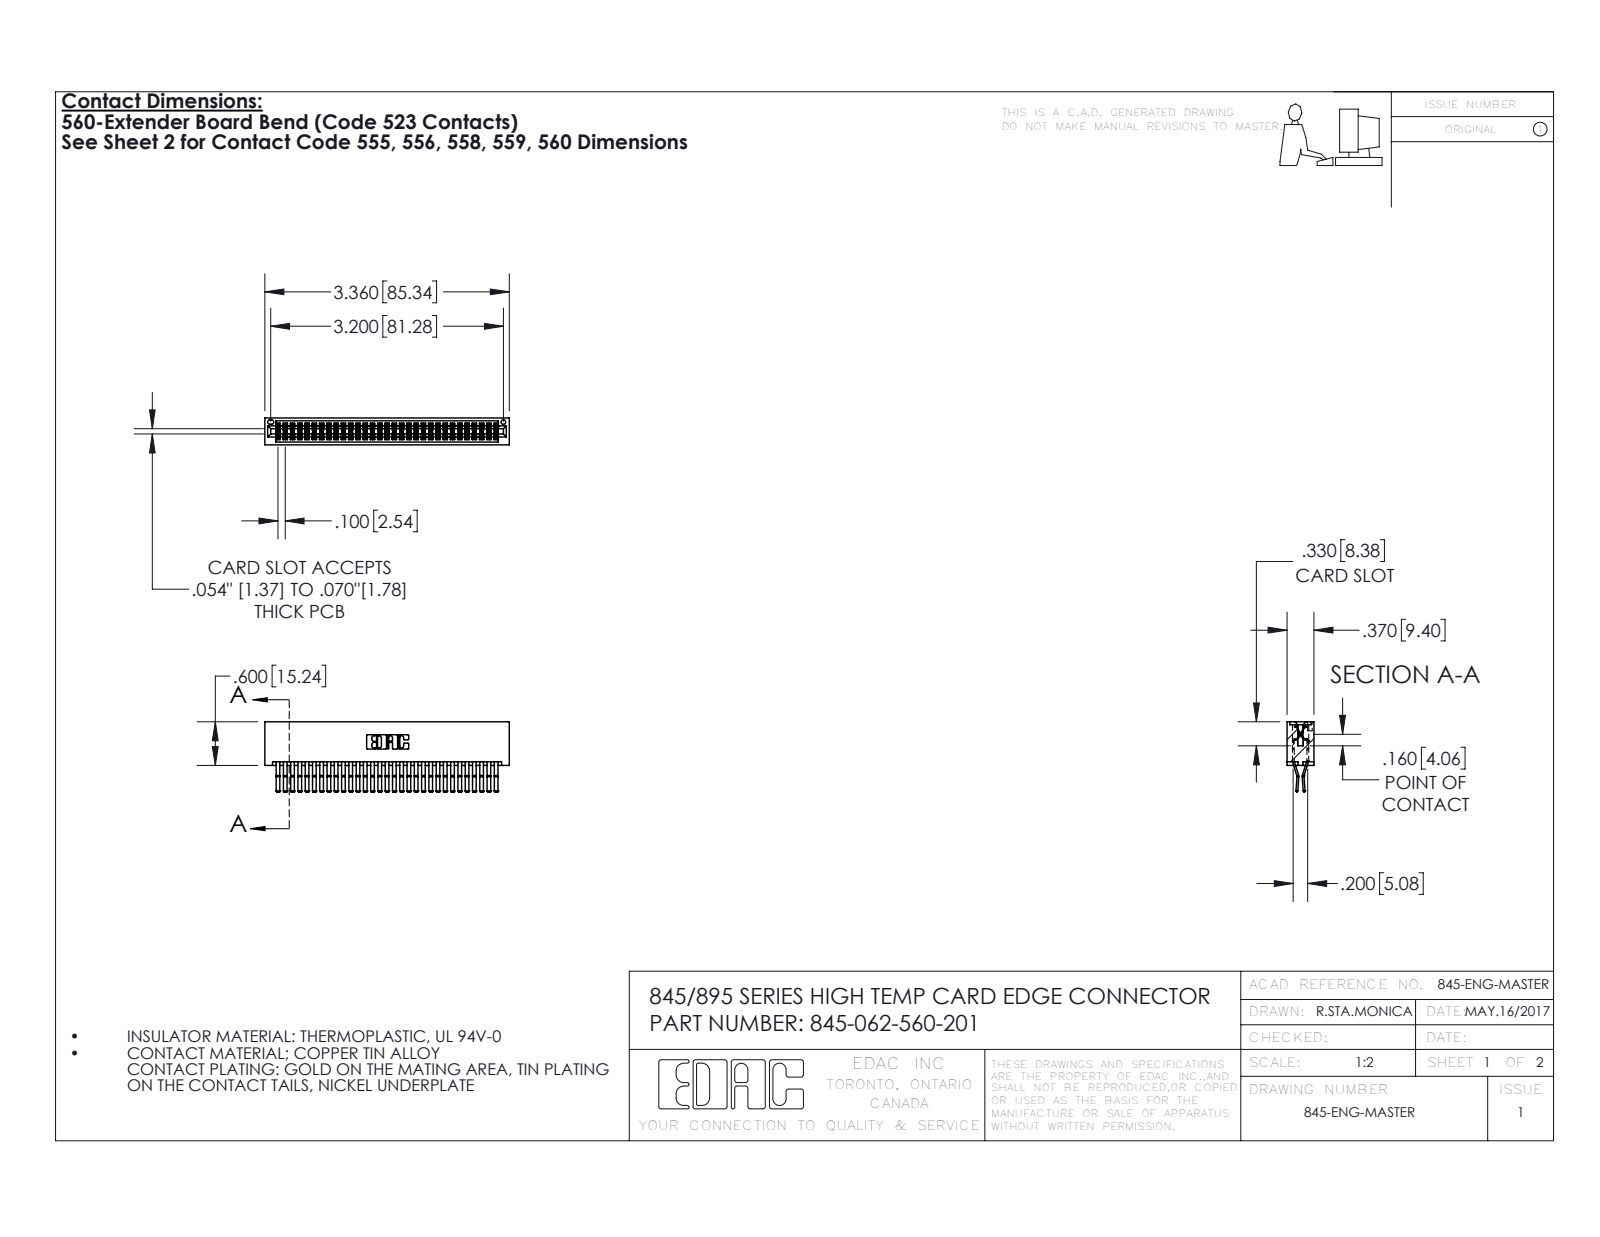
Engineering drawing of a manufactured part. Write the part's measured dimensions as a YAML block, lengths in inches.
part_name: "345-292-001_560 Tail; 345 Part_No Mounting Lugs; 345-062-560-201"
step_written_by: "SolidWorks 2016 (CONFIG_CONTROL_DESIGN)"
units: inches
bodies: {solids: 63, faces: 3342, planar: 2122, cylindrical: 1220, other: 0}
overall_size: [3.36, 0.962, 0.37]
volume: 0.562
surface_area: 22.86
round_holes:
  - {diameter: 0.064, count: 1}
partial_cylinders:
  - {radius: 0.006, count: 123}
  - {radius: 0.01, count: 22}
  - {radius: 0.007, count: 6}
  - {radius: 0.031, count: 6}
  - {radius: 0.026, count: 3}
  - {radius: 0.01, count: 2}
  - {radius: 0.014, count: 2}
  - {radius: 0.019, count: 2}
face_to_face_distances: [0.025, 0.298, 0.072, 0.2, 0.37, 0.098, 0.272, 0.225, 0.175, 0.149]
